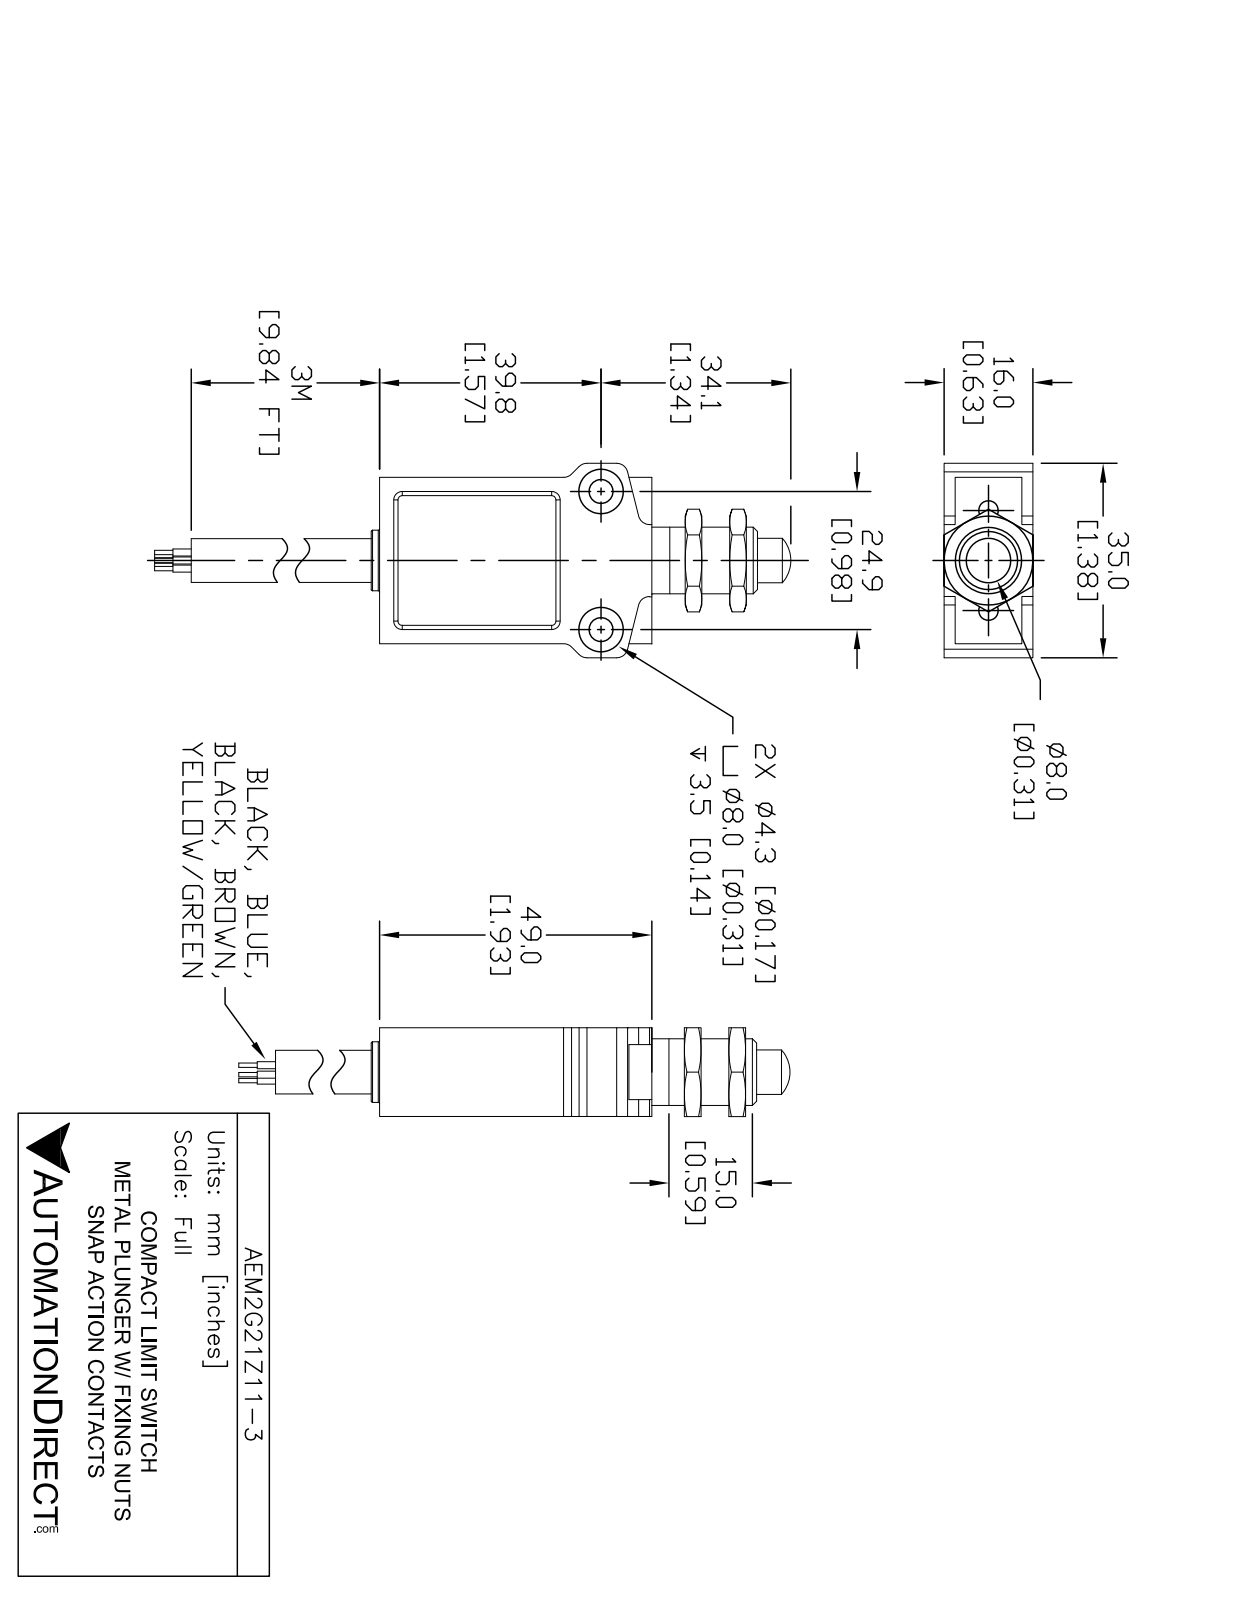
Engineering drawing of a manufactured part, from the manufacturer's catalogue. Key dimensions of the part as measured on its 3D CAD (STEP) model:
Part name (STEP PRODUCT): AEM2G21Z11-3_Default
STEP written by: SolidWorks 2021 (CONFIG_CONTROL_DESIGN)
Units: inches
Bodies: 1 solid, 168 faces (84 planar, 43 cylindrical, 41 other)
Overall size (bounding box): 3.53 × 1.38 × 0.63
Volume: 1.525 in³ · Surface area: 13.02 in²
Round holes (diameter × count): ⌀0.177 ×2, ⌀0.344 ×2
Round bosses / shafts (diameter × count): ⌀0.05 ×5, ⌀0.031 ×5, ⌀0.47 ×1, ⌀0.43 ×1, ⌀0.31 ×1
Partial cylindrical surfaces — rounded edges, fillets, slot ends (radius × count): R0.03 ×8, R0.08 ×8
Main face-to-face distances: 0.03, 0.6, 0.57, 0.63, 1.18, 0.12, 0.3, 1.93, 0.187, 0.443
Hole centre spacings: 0.98
